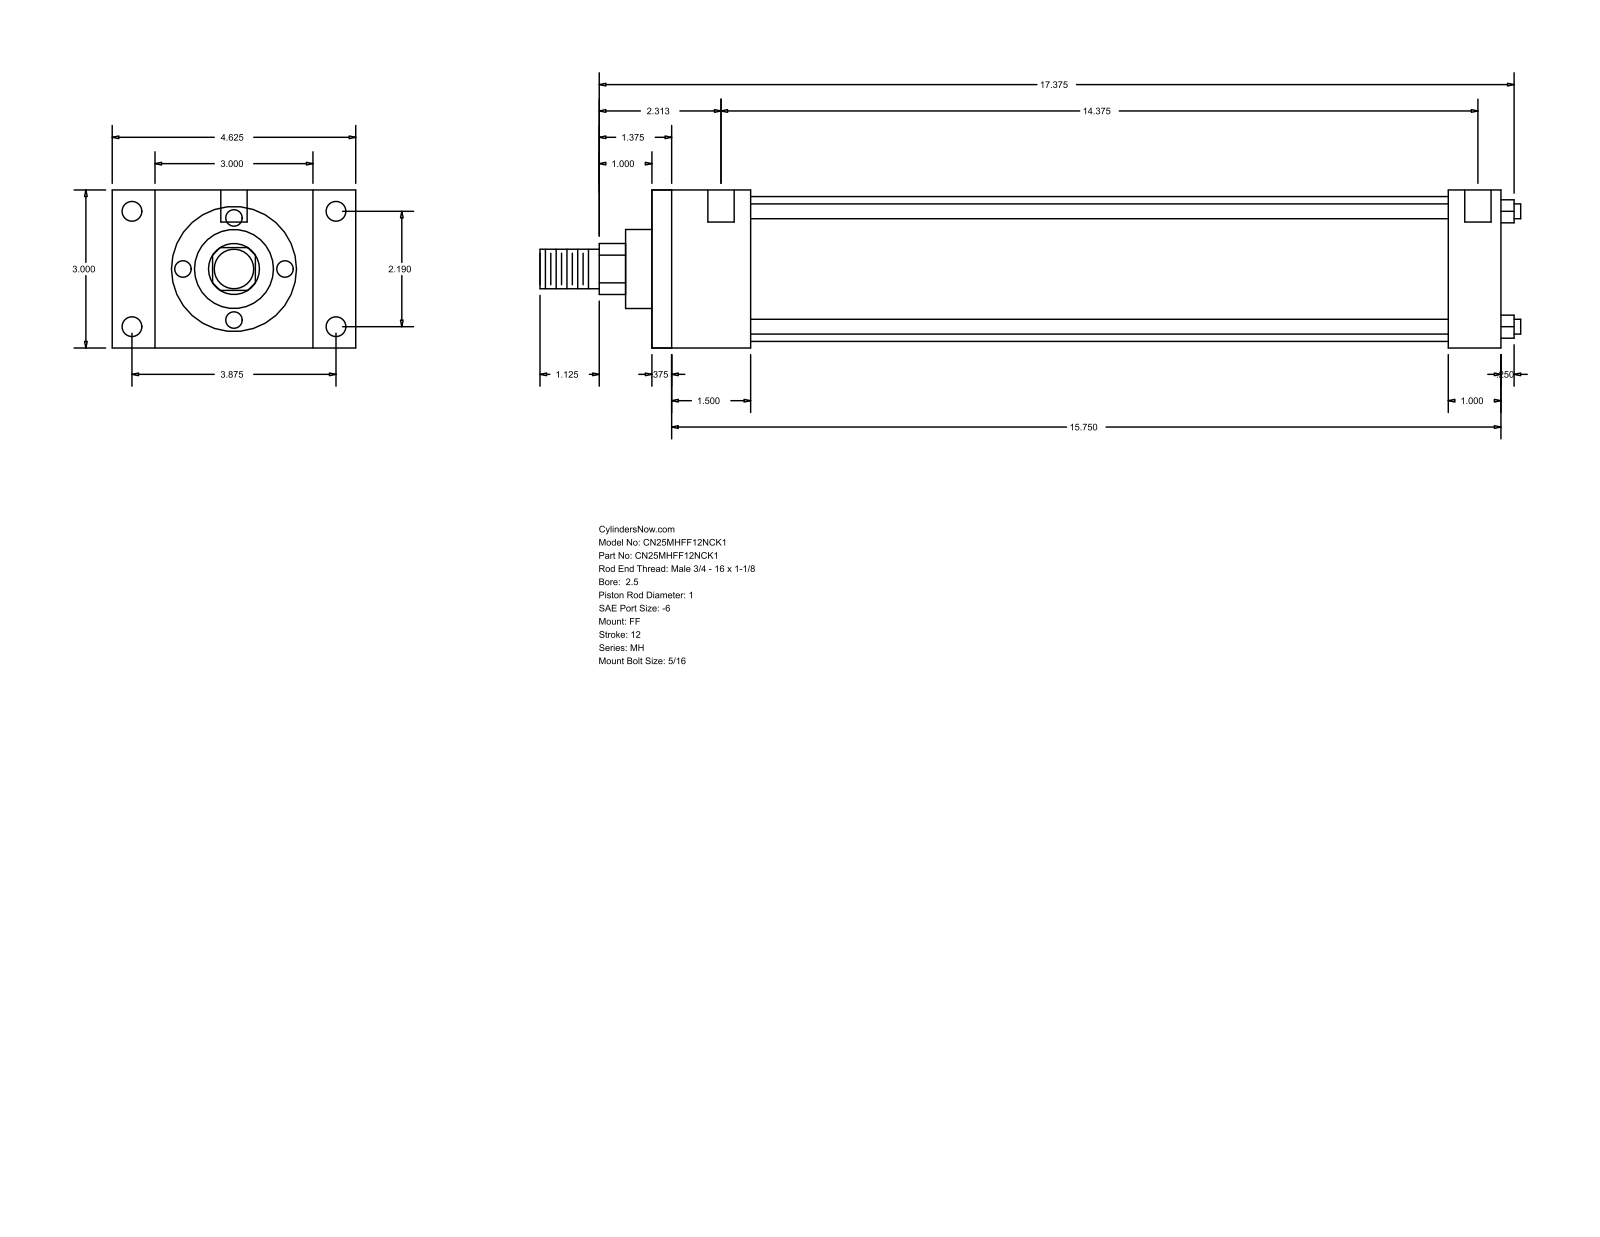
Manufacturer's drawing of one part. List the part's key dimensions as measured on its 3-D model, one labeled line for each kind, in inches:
Part name (STEP PRODUCT): MH_FF__0250_1
STEP written by: GSSL Pune (CONFIG_CONTROL_DESIGN)
Units: inches
Bodies: 0 solids, 92 faces (64 planar, 28 cylindrical, 0 other)
Overall size (bounding box): 18.625 × 4.625 × 3
Round holes (diameter × count): ⌀0.219 ×4, ⌀0.375 ×4, ⌀0.5 ×2
Round bosses / shafts (diameter × count): ⌀0.281 ×4, ⌀2.75 ×1, ⌀1.5 ×1, ⌀1 ×1, ⌀0.75 ×1
Partial cylindrical surfaces — rounded edges, fillets, slot ends (radius × count): R0.484 ×1
Main face-to-face distances: 3, 16.125, 0.375, 15.75, 1.875, 15.125, 1.5, 14.75, 13.25, 14.25
Hole centre spacings: 2.19, 3.875, 4.451, 14.687, 0.125, 0.187, 14.375, 14.5
